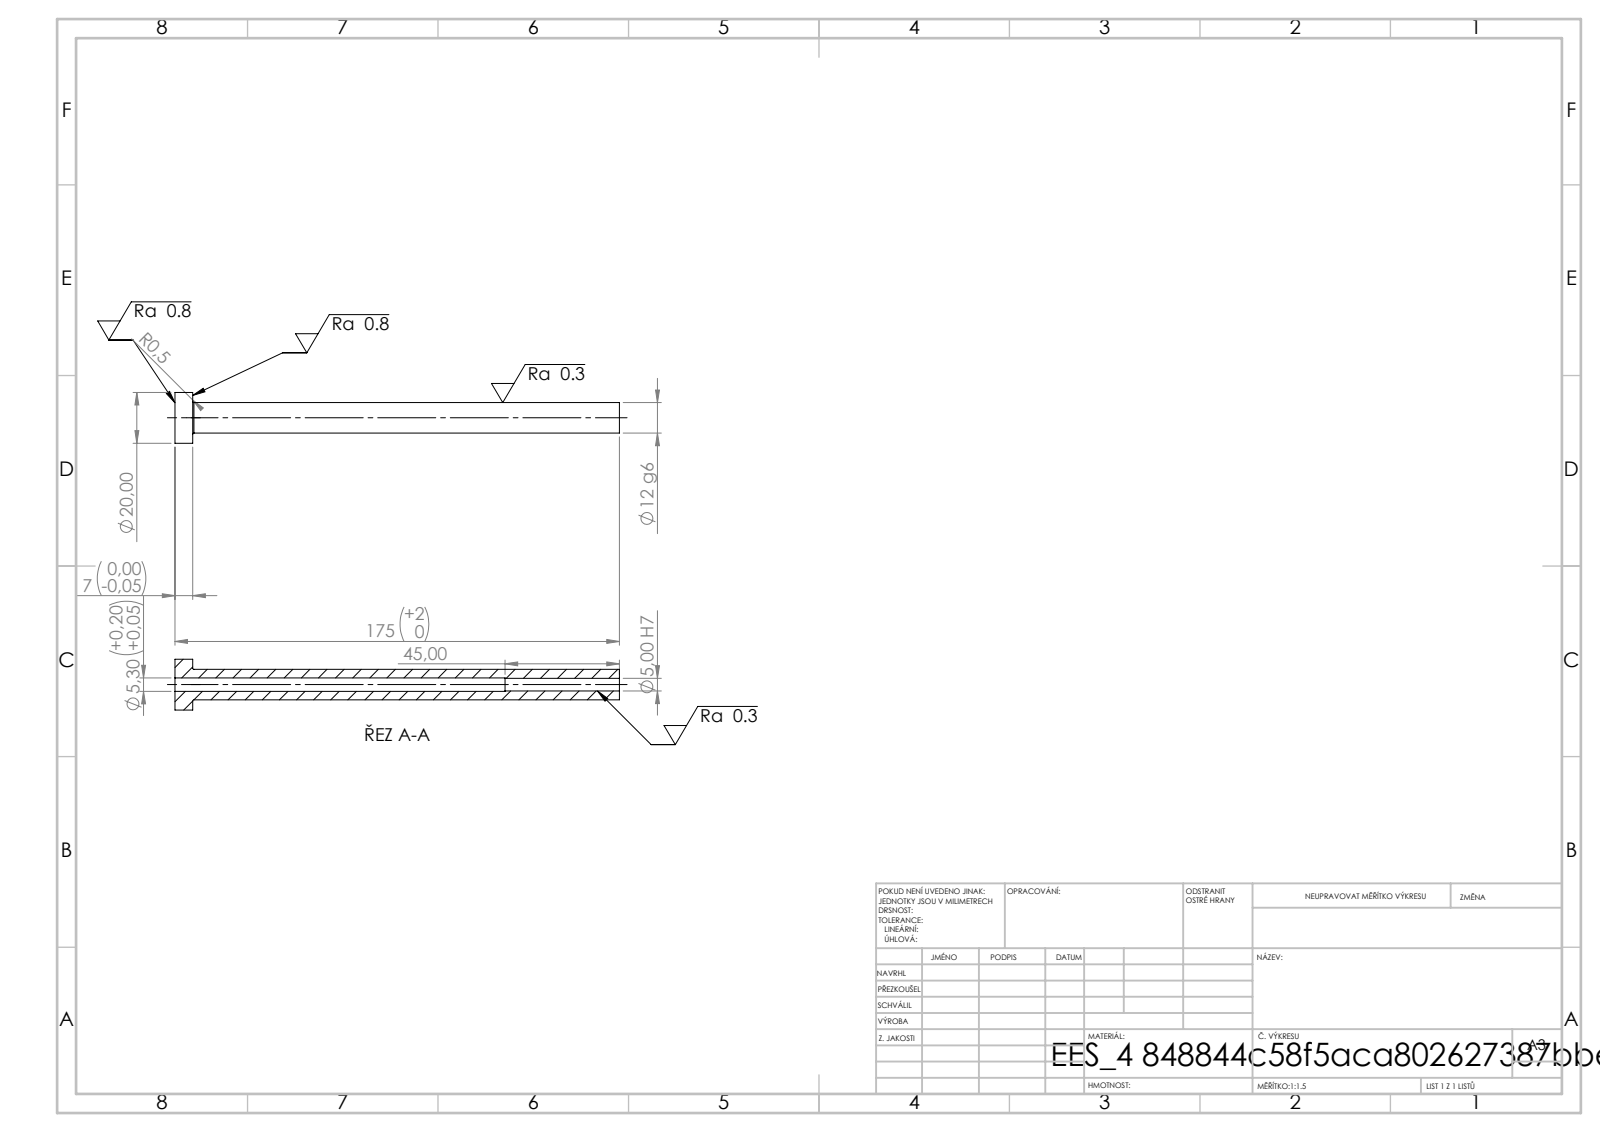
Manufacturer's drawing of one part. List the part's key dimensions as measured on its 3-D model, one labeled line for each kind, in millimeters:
STEP written by: SolidWorks 2019 (CONFIG_CONTROL_DESIGN)
Units: millimetres
Bodies: 1 solid, 14 faces (4 planar, 8 cylindrical, 2 other)
Overall size (bounding box): 175 × 20 × 20
Volume: 17 450 mm³ · Surface area: 10 226 mm²
Round holes (diameter × count): ⌀5 ×1, ⌀5.3 ×1
Round bosses / shafts (diameter × count): ⌀20 ×1, ⌀12 ×1
Main face-to-face distances: 7, 175, 168, 130, 123, 45
